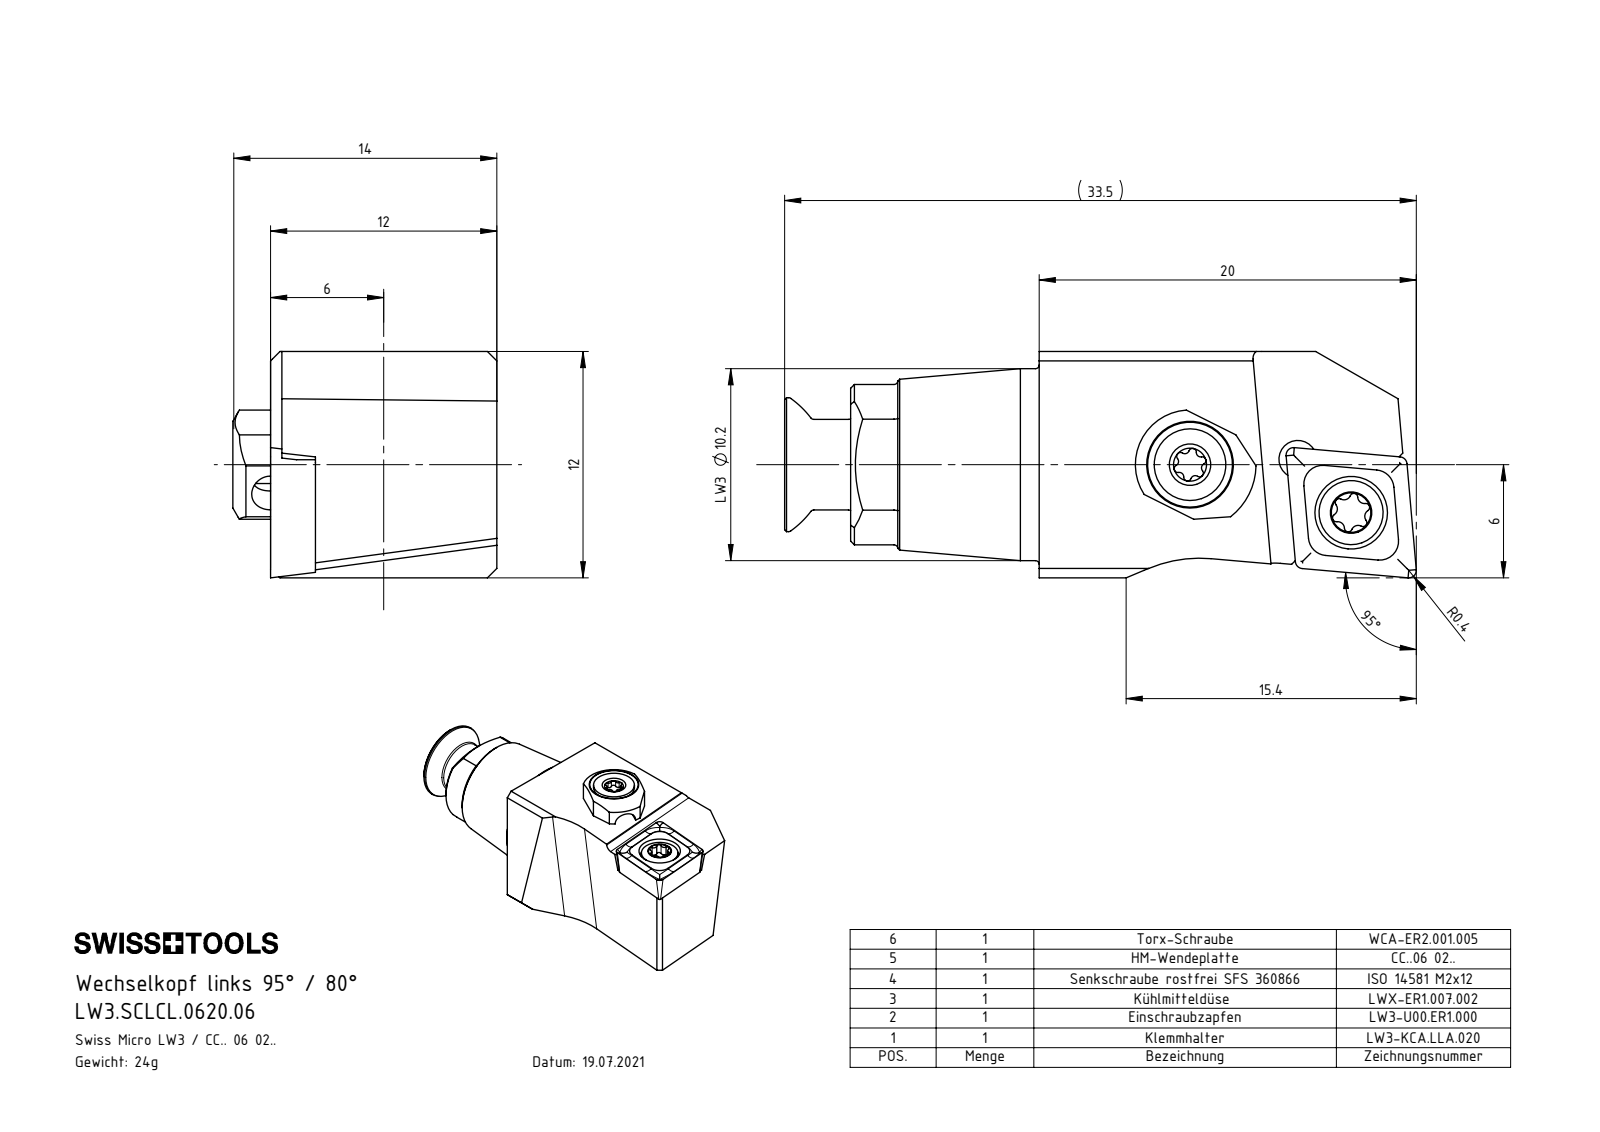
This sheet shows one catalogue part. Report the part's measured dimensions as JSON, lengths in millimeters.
{"part_name": "LWX-ER1.007.002; LW3-U00.ER1.000_B; ISO 14581 - M2x12; CCMT060204 (+3 more)", "step_written_by": "SolidWorks 2022 (CONFIG_CONTROL_DESIGN)", "units": "millimeters", "bodies": {"solids": 6, "faces": 251, "planar": 69, "cylindrical": 78, "other": 104}, "overall_size": [33.4, 14, 12], "volume_mm3": 3025, "surface_area_mm2": 2389, "round_holes": [[2, 2], [1.6, 1], [2.05, 1], [2.5, 1], [2.8, 1], [3, 1], [3.85, 1], [5.5, 1]], "round_bosses_or_shafts": [[10.18, 1], [6.9, 1], [6, 1], [5, 1], [4.8, 1], [3.8, 1], [3.4, 1], [2.5, 1]], "partial_cylinders_radius": [[0.2, 8], [0.21, 6], [0.24, 6], [0.36, 5], [0.36, 1], [0.5, 1], [1, 1], [2.9, 1]], "face_to_face_distances": [12, 11.4, 9.62, 2.38, 1.78, 0.6, 2, 2.5, 13.4, 7], "hole_center_spacings": [3.92, 4.02, 5.72, 8.84, 8.92]}
